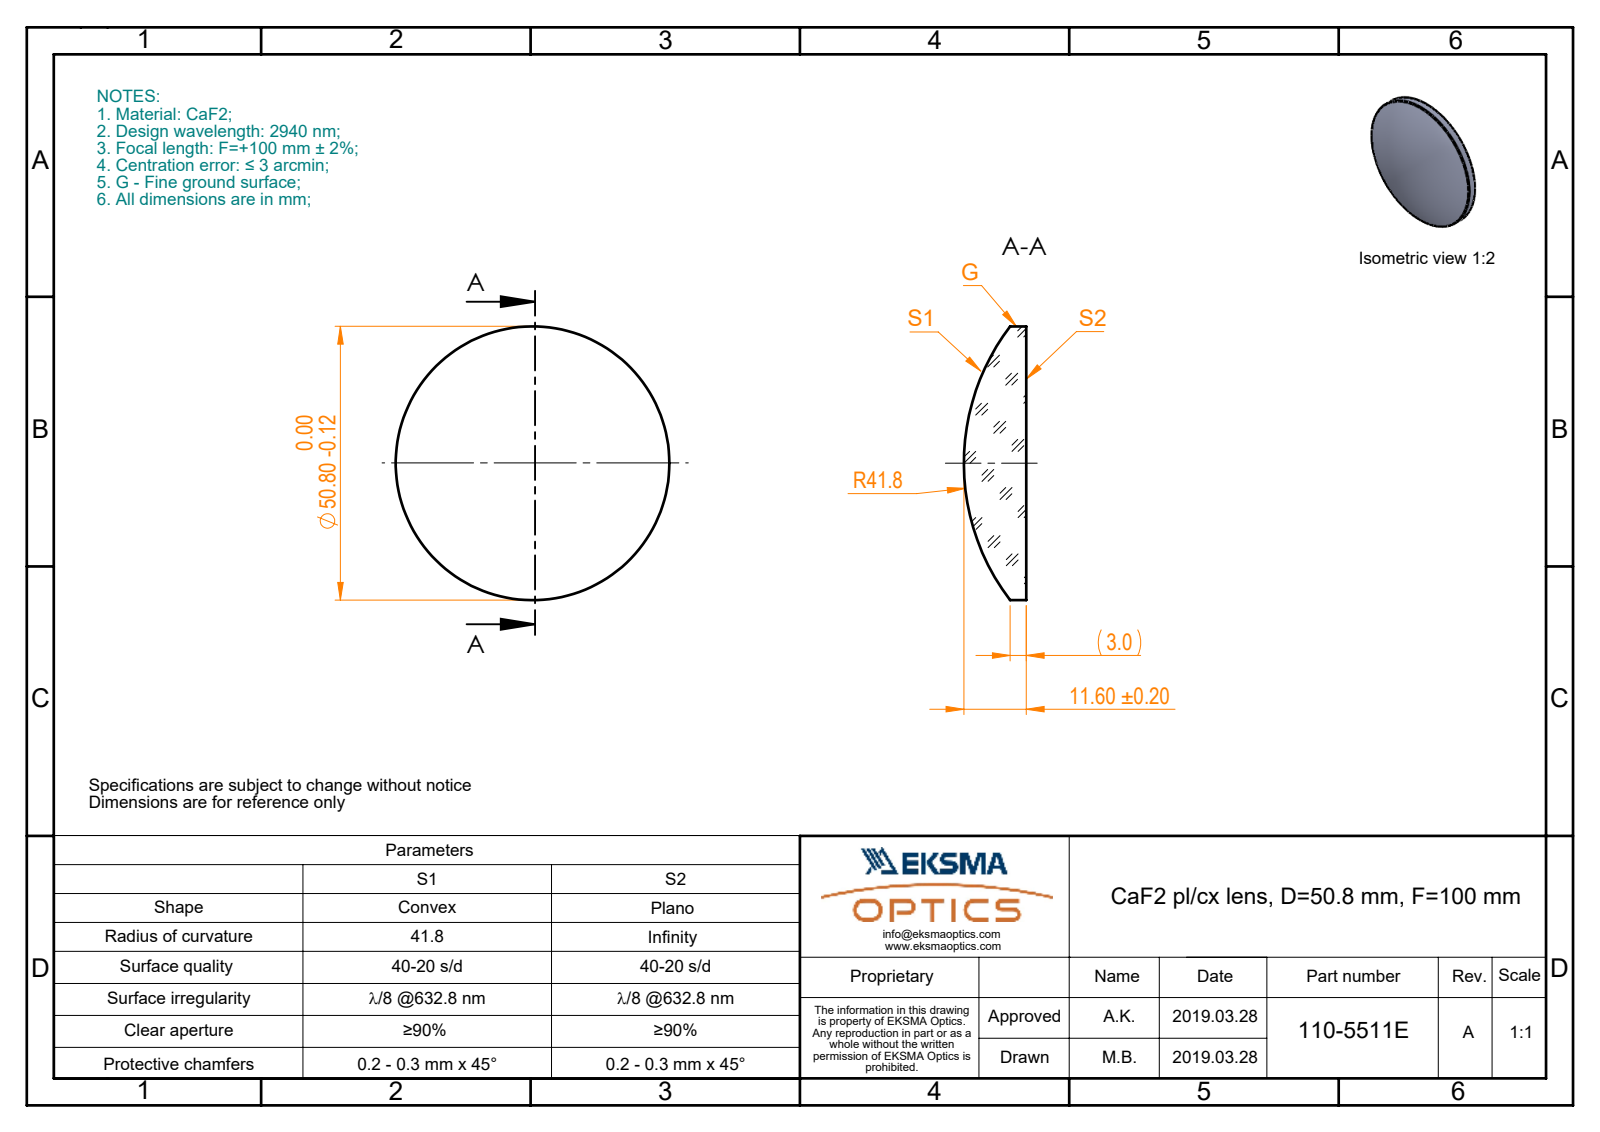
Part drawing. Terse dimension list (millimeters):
name: 110-5511E CaF2 pl-cx 50.8 F100
written by: SolidWorks 2017 (CONFIG_CONTROL_DESIGN)
unit: mm
bodies: 1 solid, 5 faces (1 planar, 2 cylindrical, 2 other)
size: 50.8 × 50.8 × 11.6
volume: 15 134 mm³; area: 4 765 mm²
bosses: 1× ⌀50.8
